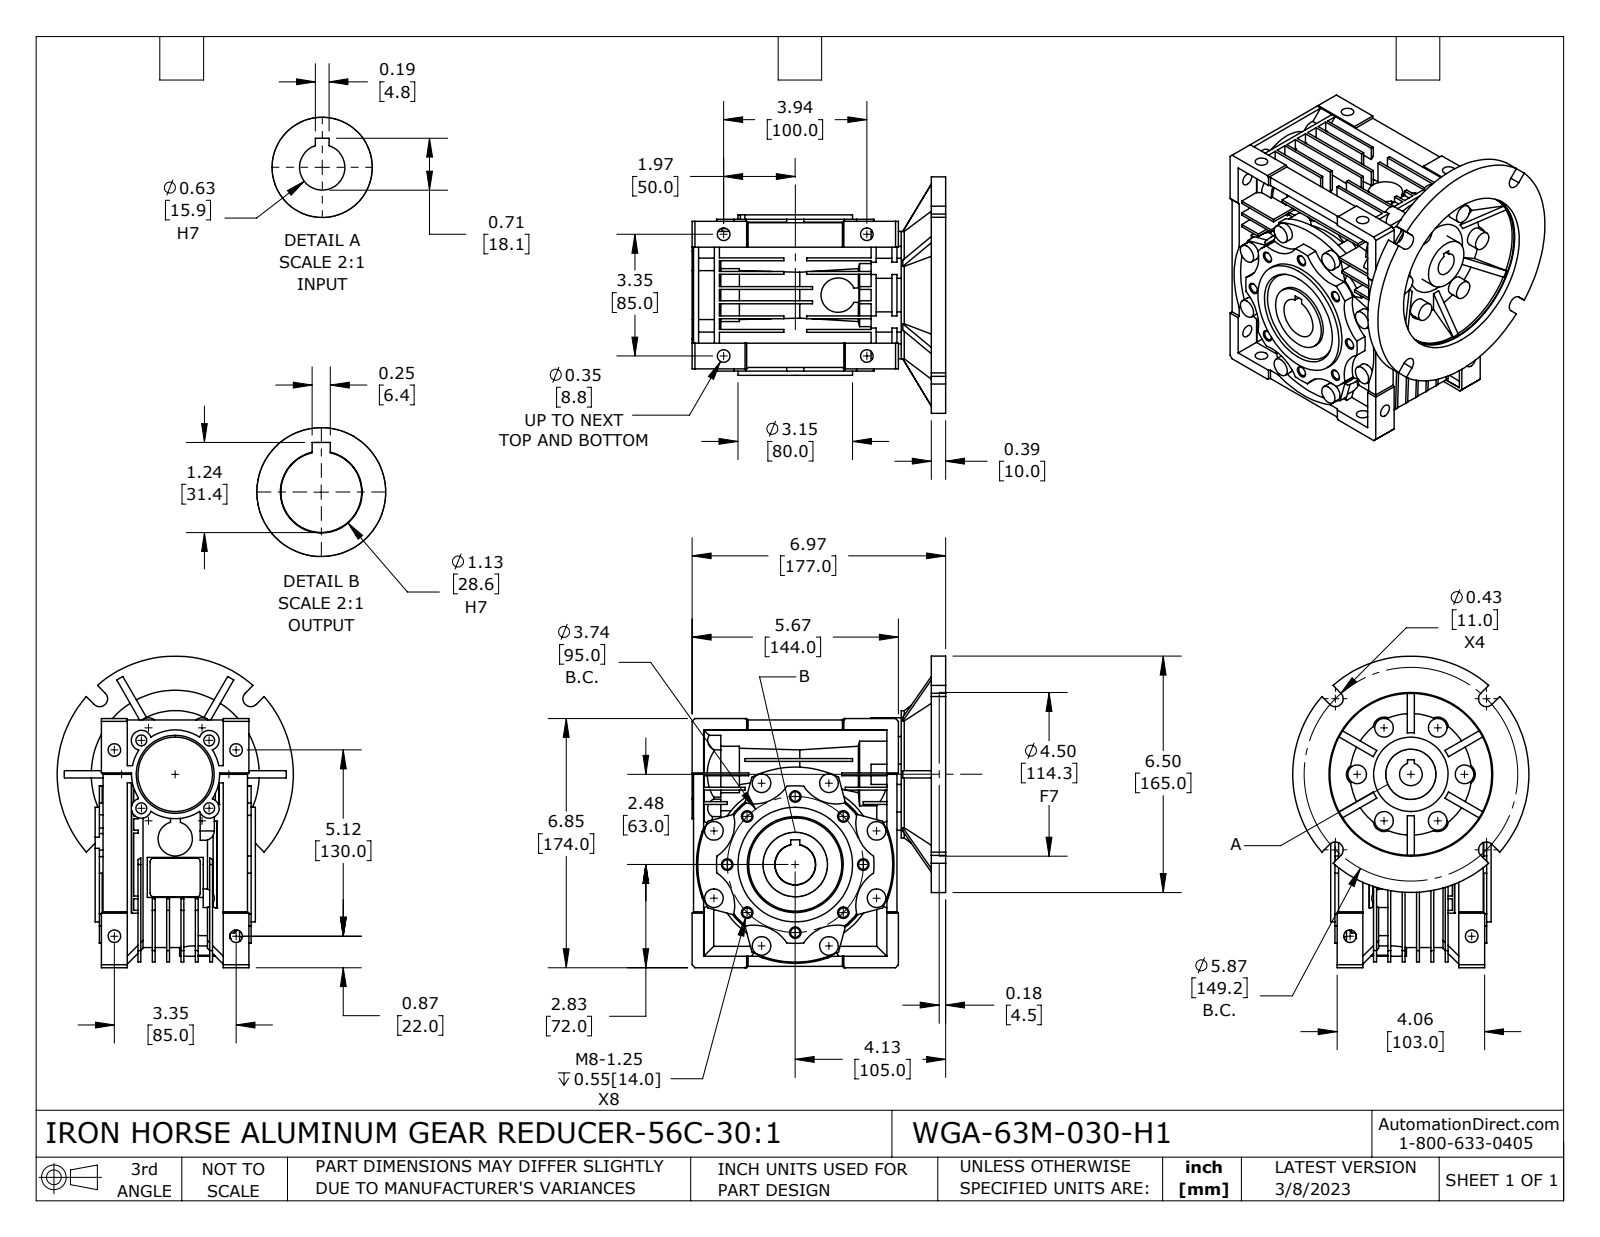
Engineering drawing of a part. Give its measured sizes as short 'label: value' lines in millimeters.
name: WGA-63M-030-H1
written by: SolidWorks 2021 (CONFIG_CONTROL_DESIGN)
unit: mm
bodies: 4 solids, 1231 faces (759 planar, 331 cylindrical, 141 other)
size: 217.5 × 177 × 165
volume: 1 917 000 mm³; area: 366 500 mm²
holes: 8× ⌀6.7, 8× ⌀6.7, 8× ⌀8.8, 4× ⌀7.6, 1× ⌀15.9, 1× ⌀16.5, 1× ⌀28.6, 1× ⌀34, 1× ⌀37, 1× ⌀45, 1× ⌀52, 1× ⌀113
bosses: 14× ⌀13, 3× ⌀24, 1× ⌀165, 1× ⌀110, 1× ⌀89, 1× ⌀80, 1× ⌀69, 1× ⌀62
rounds: 10× R7, 8× R27, 6× R7.5, 4× R2.5, 4× R5.5, 1× R8.4, 1× R29.5, 1× R30.5
face distances: 10, 8, 20, 2, 30, 7, 12, 18, 40, 31
hole spacings: 36.3, 47.5, 67.2, 87.8, 33.5, 47.4, 85, 20
